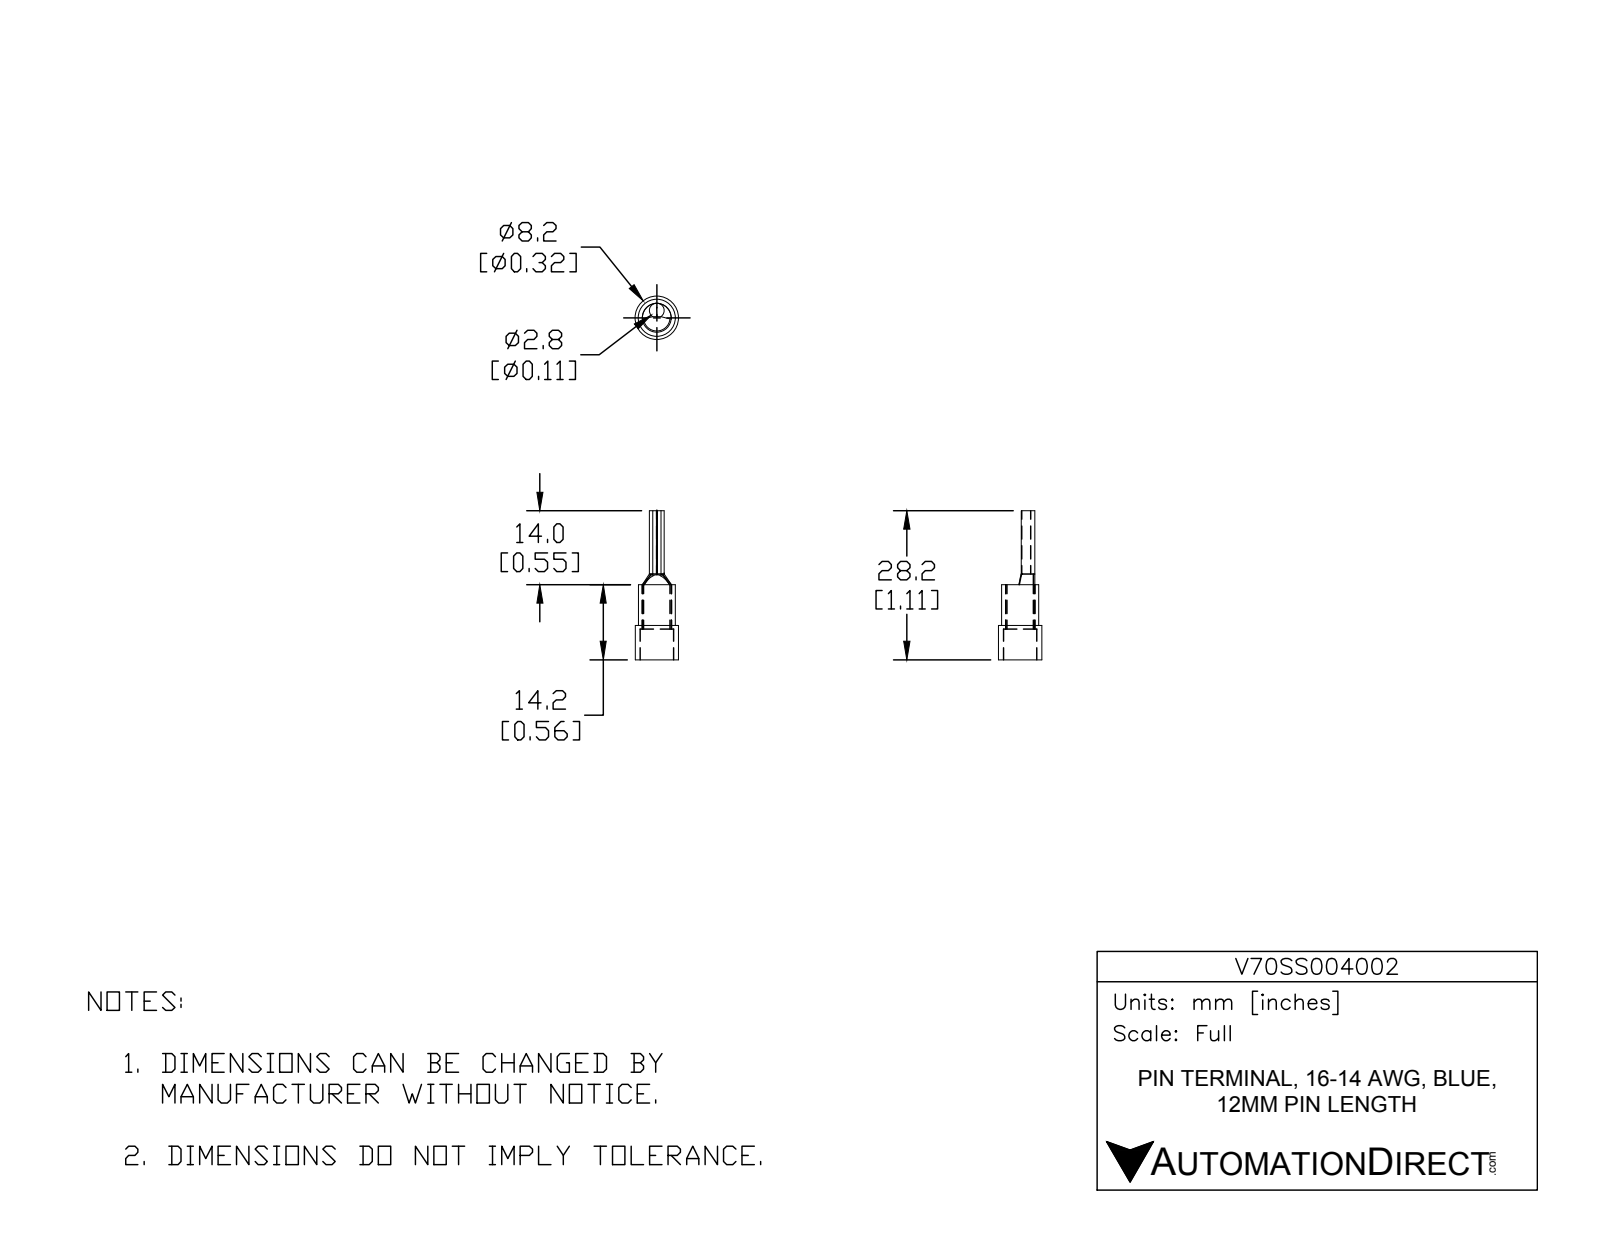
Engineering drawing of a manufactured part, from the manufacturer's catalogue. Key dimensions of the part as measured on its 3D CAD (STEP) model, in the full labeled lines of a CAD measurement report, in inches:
Part name (STEP PRODUCT): V70SS004003
STEP written by: SolidWorks 2017 (AUTOMOTIVE_DESIGN)
Units: inches
Bodies: 4 solids, 43 faces (21 planar, 16 cylindrical, 6 other)
Overall size (bounding box): 1.11 × 0.323 × 0.323
Volume: 0.022 in³ · Surface area: 1.765 in²
Round holes (diameter × count): ⌀0.197 ×1, ⌀0.217 ×1, ⌀0.248 ×1
Round bosses / shafts (diameter × count): ⌀0.323 ×1, ⌀0.276 ×1, ⌀0.11 ×1
Partial cylindrical surfaces — rounded edges, fillets, slot ends (radius × count): R0.004 ×2
Main face-to-face distances: 0.559, 0.256, 0.303, 0.228, 0.028, 0.331, 0.638, 0.409, 0.382, 0.079
